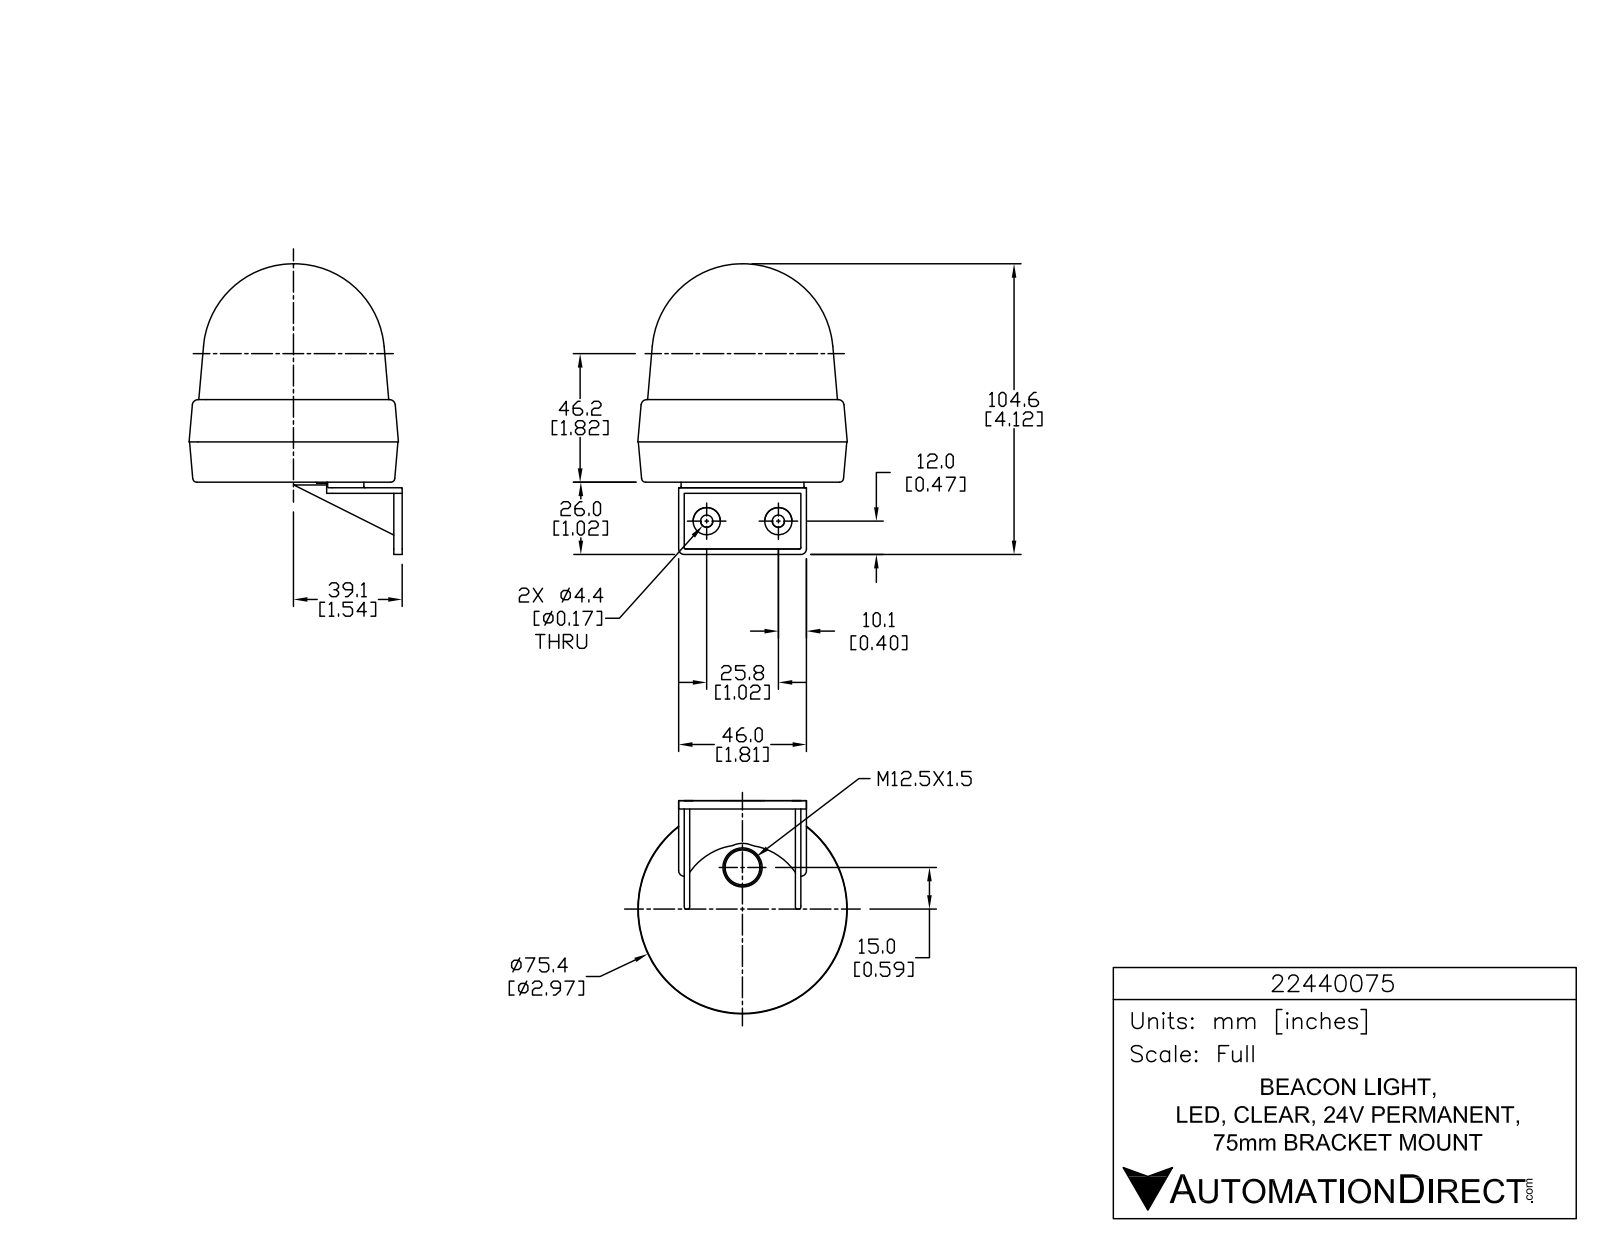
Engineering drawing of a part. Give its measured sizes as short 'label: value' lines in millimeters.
name: 22440075
written by: SolidWorks 2015 (AUTOMOTIVE_DESIGN)
unit: mm
bodies: 1 solid, 819 faces (549 planar, 180 cylindrical, 90 other)
size: 104.6 × 82.6 × 75.4
volume: 262 500 mm³; area: 27 080 mm²
holes: 3× ⌀1.5, 2× ⌀4.4
bosses: 3× ⌀8.6, 3× ⌀2.1, 2× ⌀9.8
rounds: 9× R0.1, 6× R0.1, 6× R0.3, 6× R0.3, 6× R0.3, 6× R0.5, 6× R5, 4× R2
face distances: 2, 4, 40, 1, 3, 42, 38, 2, 42, 44
hole spacings: 25.8
